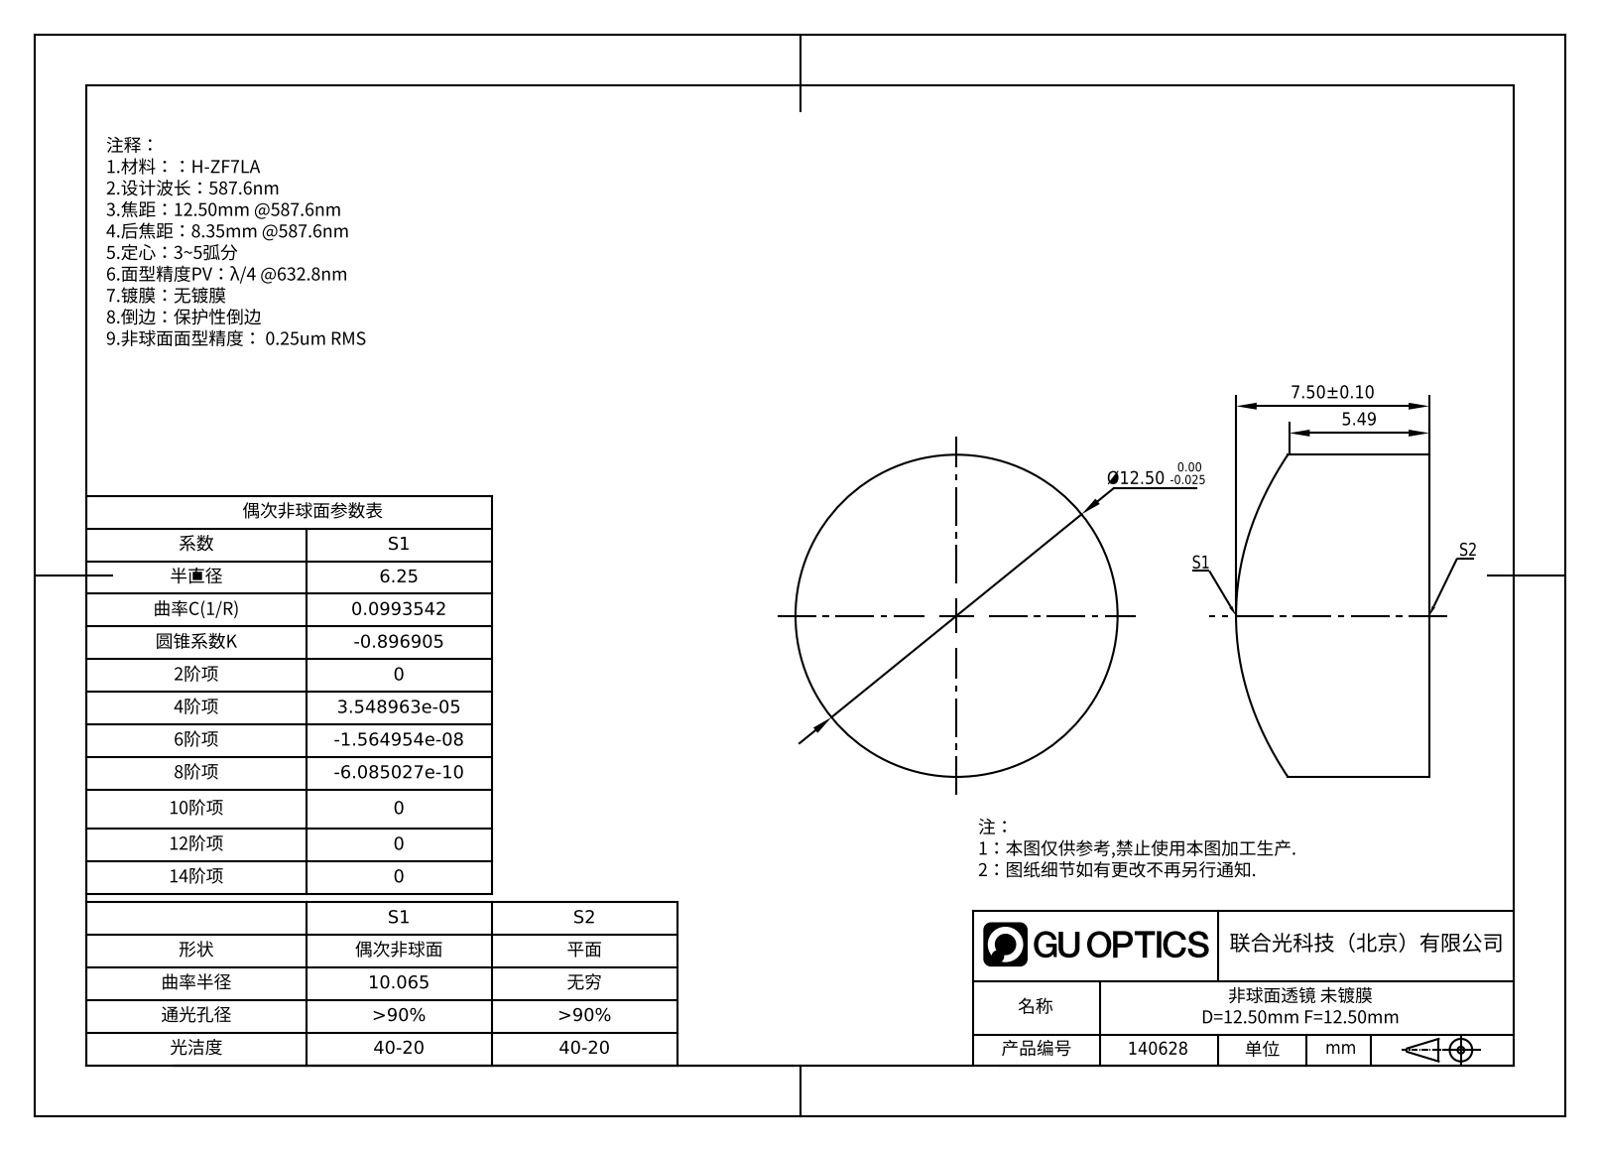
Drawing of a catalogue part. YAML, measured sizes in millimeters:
part_name: "GLA11-012-012-H; surfaces 1,2.stp; GLA11-012-012-H.stp"
step_written_by: "SolidWorks 2023 (CONFIG_CONTROL_DESIGN)"
units: millimeters
bodies: {solids: 1, faces: 5, planar: 1, cylindrical: 2, other: 2}
overall_size: [12.5, 12.5, 7.5]
volume: 798
surface_area: 473
round_bosses_or_shafts:
  - {diameter: 12.5, count: 1}
